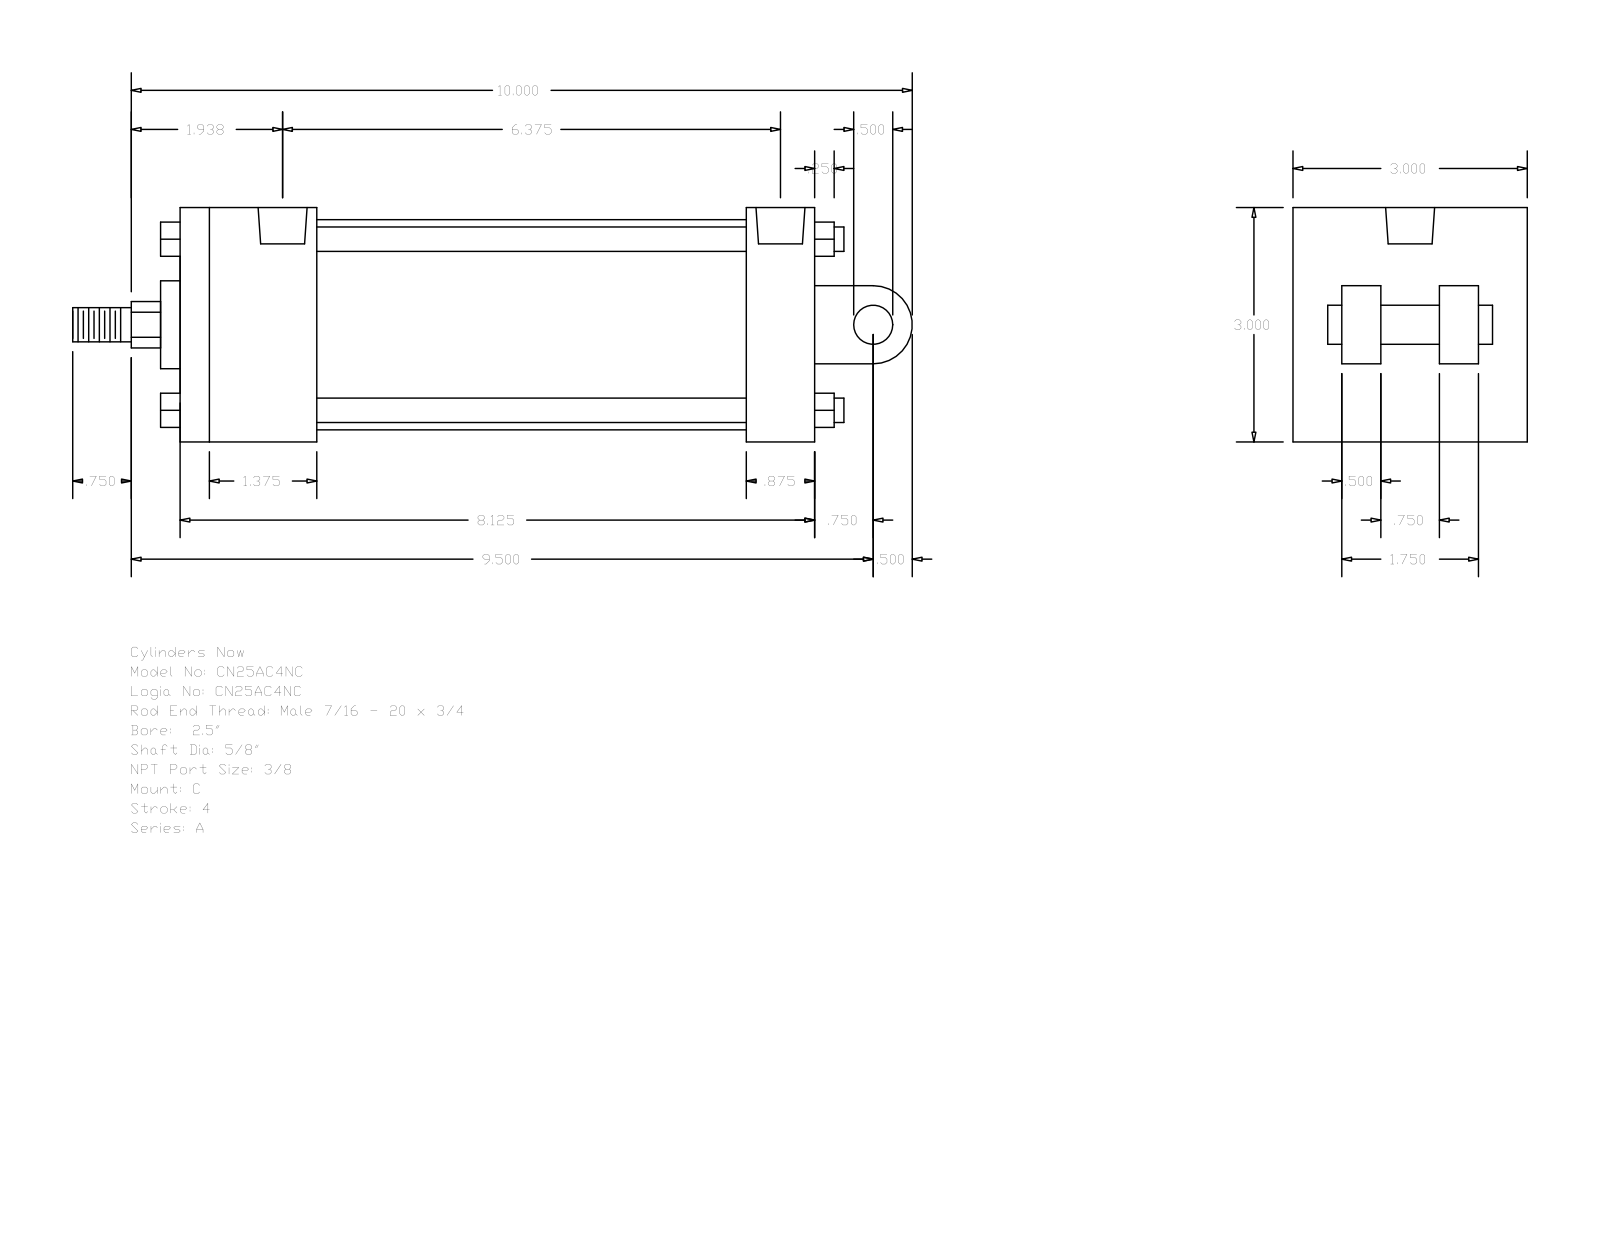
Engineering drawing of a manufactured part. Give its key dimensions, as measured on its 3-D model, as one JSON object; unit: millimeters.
{"part_name": "A_C__0250_0.625", "step_written_by": "GSSL Pune (CONFIG_CONTROL_DESIGN)", "units": "millimeters", "bodies": {"solids": 0, "faces": 135, "planar": 102, "cylindrical": 33, "other": 0}, "overall_size": [273.05, 76.2, 76.2], "round_holes": [[5.56, 4], [15.93, 2]], "round_bosses_or_shafts": [[7.94, 4], [68.33, 1], [28.57, 1], [15.88, 1], [12.7, 1], [11.11, 1]], "partial_cylinders_radius": [[7.54, 1], [12.7, 1]], "face_to_face_distances": [76.2, 206.37, 44.45, 184.15, 139.7, 161.92, 22.22, 50.8, 12.7, 25.4], "hole_center_spacings": [2.38, 164.31, 166.69, 161.93]}
